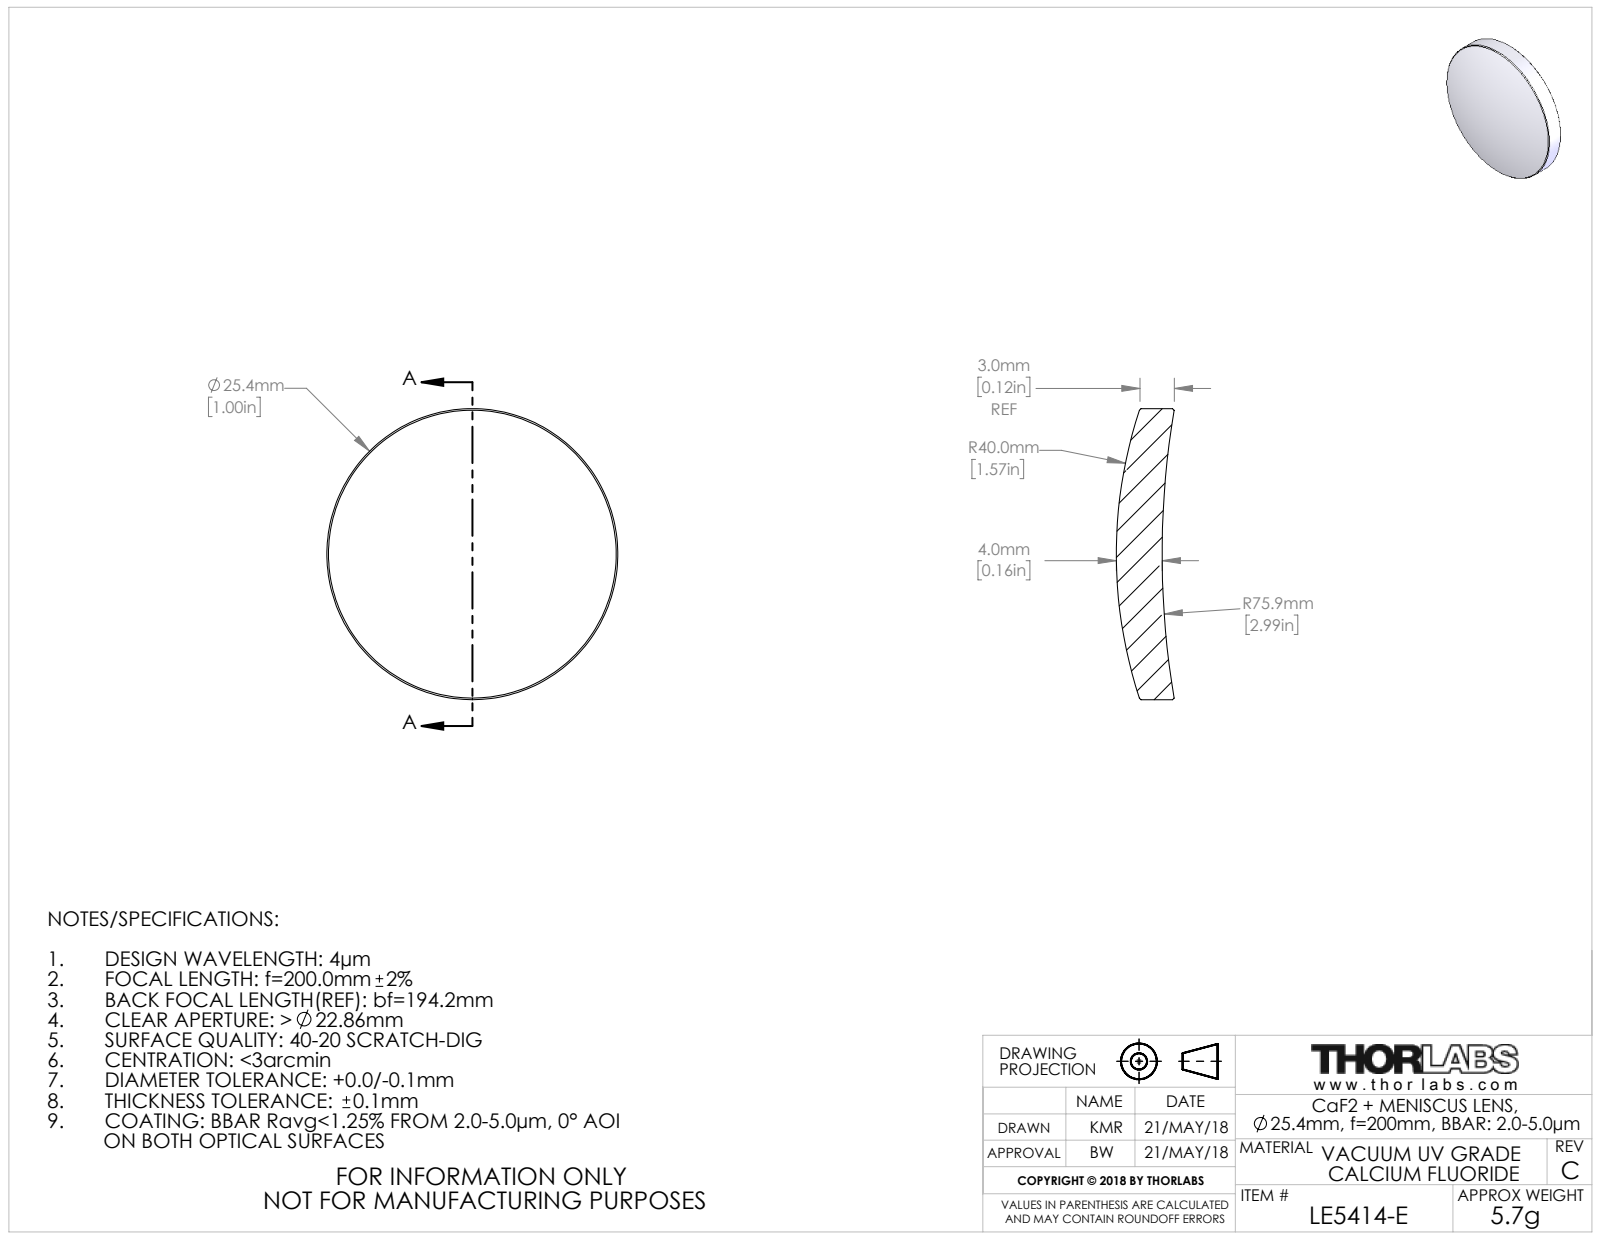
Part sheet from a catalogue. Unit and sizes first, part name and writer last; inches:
Units: inches
Overall size (bounding box): 1 × 1 × 0.199
Round bosses / shafts (diameter × count): ⌀1 ×1
Volume: 0.108 in³ · Surface area: 1.949 in²
Bodies: 1 solid, 10 faces (0 planar, 2 cylindrical, 8 other)
Part name (STEP PRODUCT): 20165-E0W
STEP written by: SolidWorks 2016 (CONFIG_CONTROL_DESIGN)
